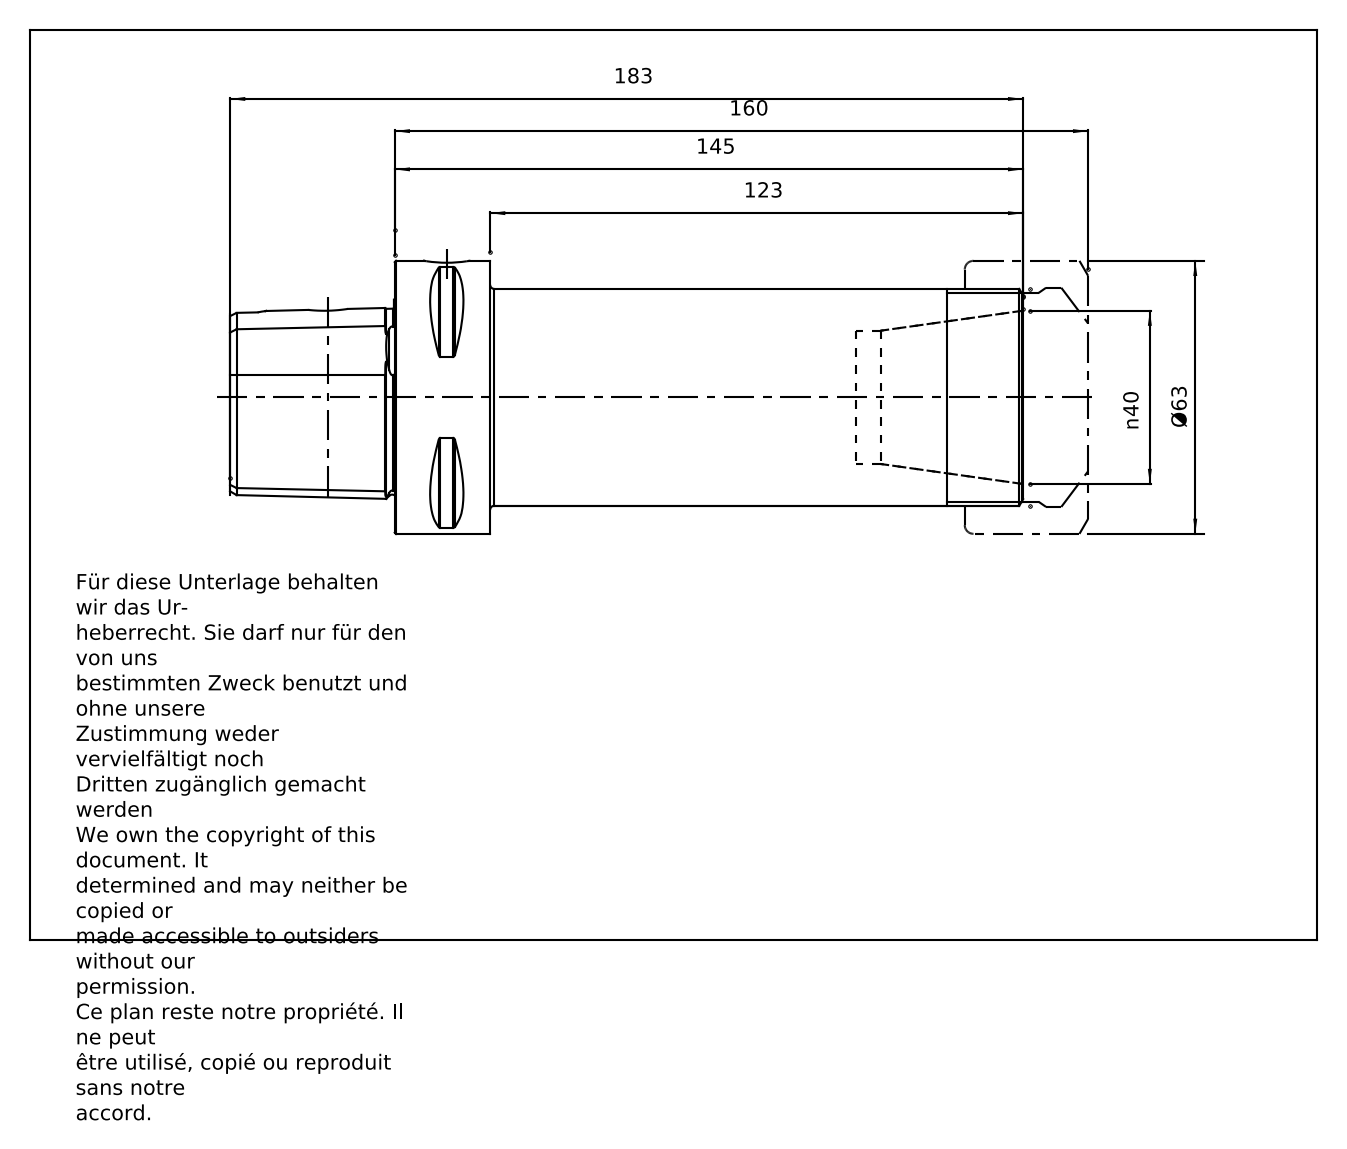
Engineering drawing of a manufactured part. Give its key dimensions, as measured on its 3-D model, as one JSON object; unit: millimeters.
{"part_name": "CC6-022-40; 83-912-40; CC6-022-40_ASM", "step_written_by": "PRO/ENGINEER BY PARAMETRIC TECHNOLOGY CORPORATION, 2010430 (CONFIG_CONTROL_DESIGN)", "units": "millimeters", "bodies": {"solids": 2, "faces": 164, "planar": 51, "cylindrical": 41, "other": 72}, "overall_size": [198, 63, 63], "volume_mm3": 376532, "surface_area_mm2": 55261, "round_holes": [[4.25, 1], [8.1, 1], [10.04, 1], [18, 1], [28.02, 1], [30.5, 1], [32, 1]], "round_bosses_or_shafts": [[63, 1], [50, 1], [20, 1]], "partial_cylinders_radius": [[0.5, 8], [2.7, 6], [6, 1]], "face_to_face_distances": [25.5, 134.5, 160, 38, 145, 22, 112.5, 138, 107, 85], "hole_center_spacings": [27.5]}
